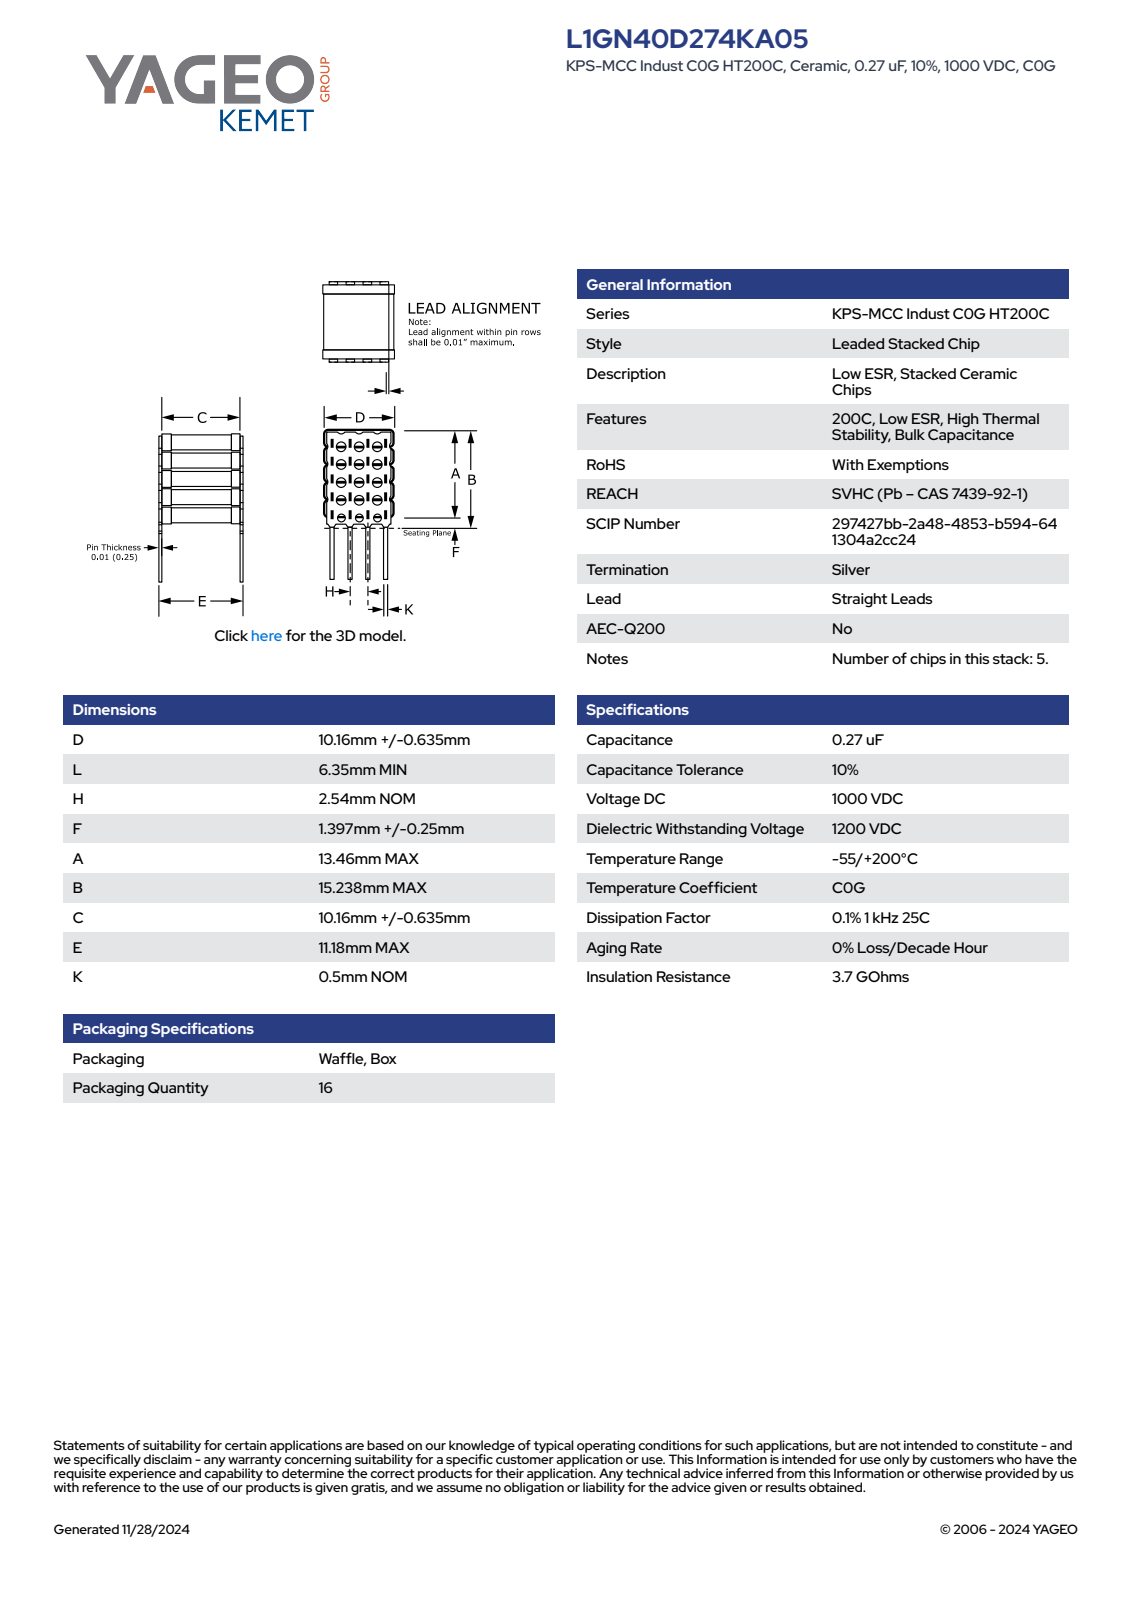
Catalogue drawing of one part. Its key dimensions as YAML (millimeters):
part_name: "CCSS_LSN4_4_D10.795L6.35H2.54F1.647A13.46B15.238C10.795E11.18K0.5"
step_written_by: "SolidWorks 2014 (AUTOMOTIVE_DESIGN)"
units: millimeters
bodies: {solids: 4, faces: 215, planar: 215, cylindrical: 0, other: 0}
overall_size: [21.59, 11.25, 10.79]
volume: 1544
surface_area: 1912
face_to_face_distances: [2.69, 5.39, 5.38, 8.08, 5.26, 2.62, 5.31, 2.57, 2.74, 2.49]
